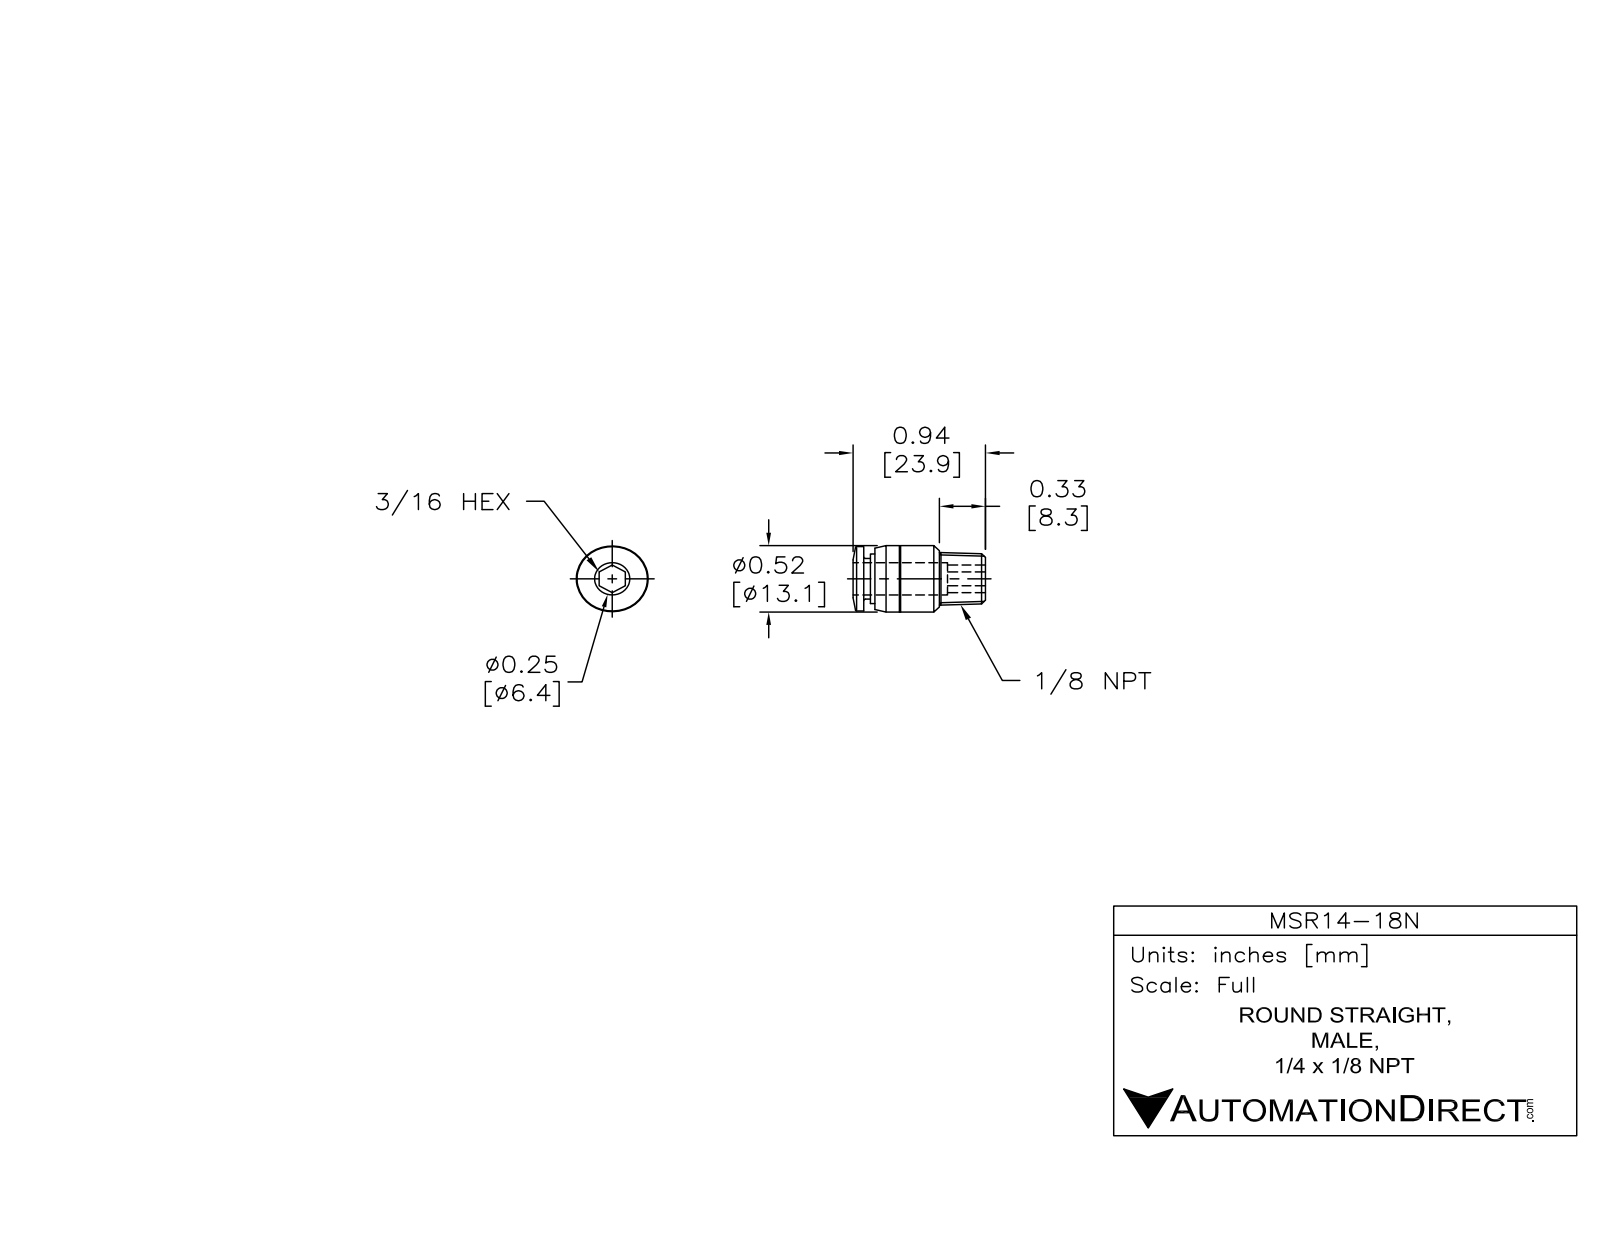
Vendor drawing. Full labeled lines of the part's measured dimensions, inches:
Part name (STEP PRODUCT): MSR14-18N
STEP written by: SolidWorks 2015 (AUTOMOTIVE_DESIGN)
Units: inches
Bodies: 1 solid, 42 faces (6 planar, 14 cylindrical, 22 other)
Overall size (bounding box): 0.933 × 0.512 × 0.512
Volume: 0.108 in³ · Surface area: 2.487 in²
Round holes (diameter × count): ⌀0.189 ×1, ⌀0.258 ×1
Round bosses / shafts (diameter × count): ⌀0.512 ×1, ⌀0.496 ×1, ⌀0.382 ×1, ⌀0.313 ×1
Main face-to-face distances: 0.079, 0.78, 0.858, 0.811, 0.031, 0.047, 0.268, 0.512, 0.543, 0.591
